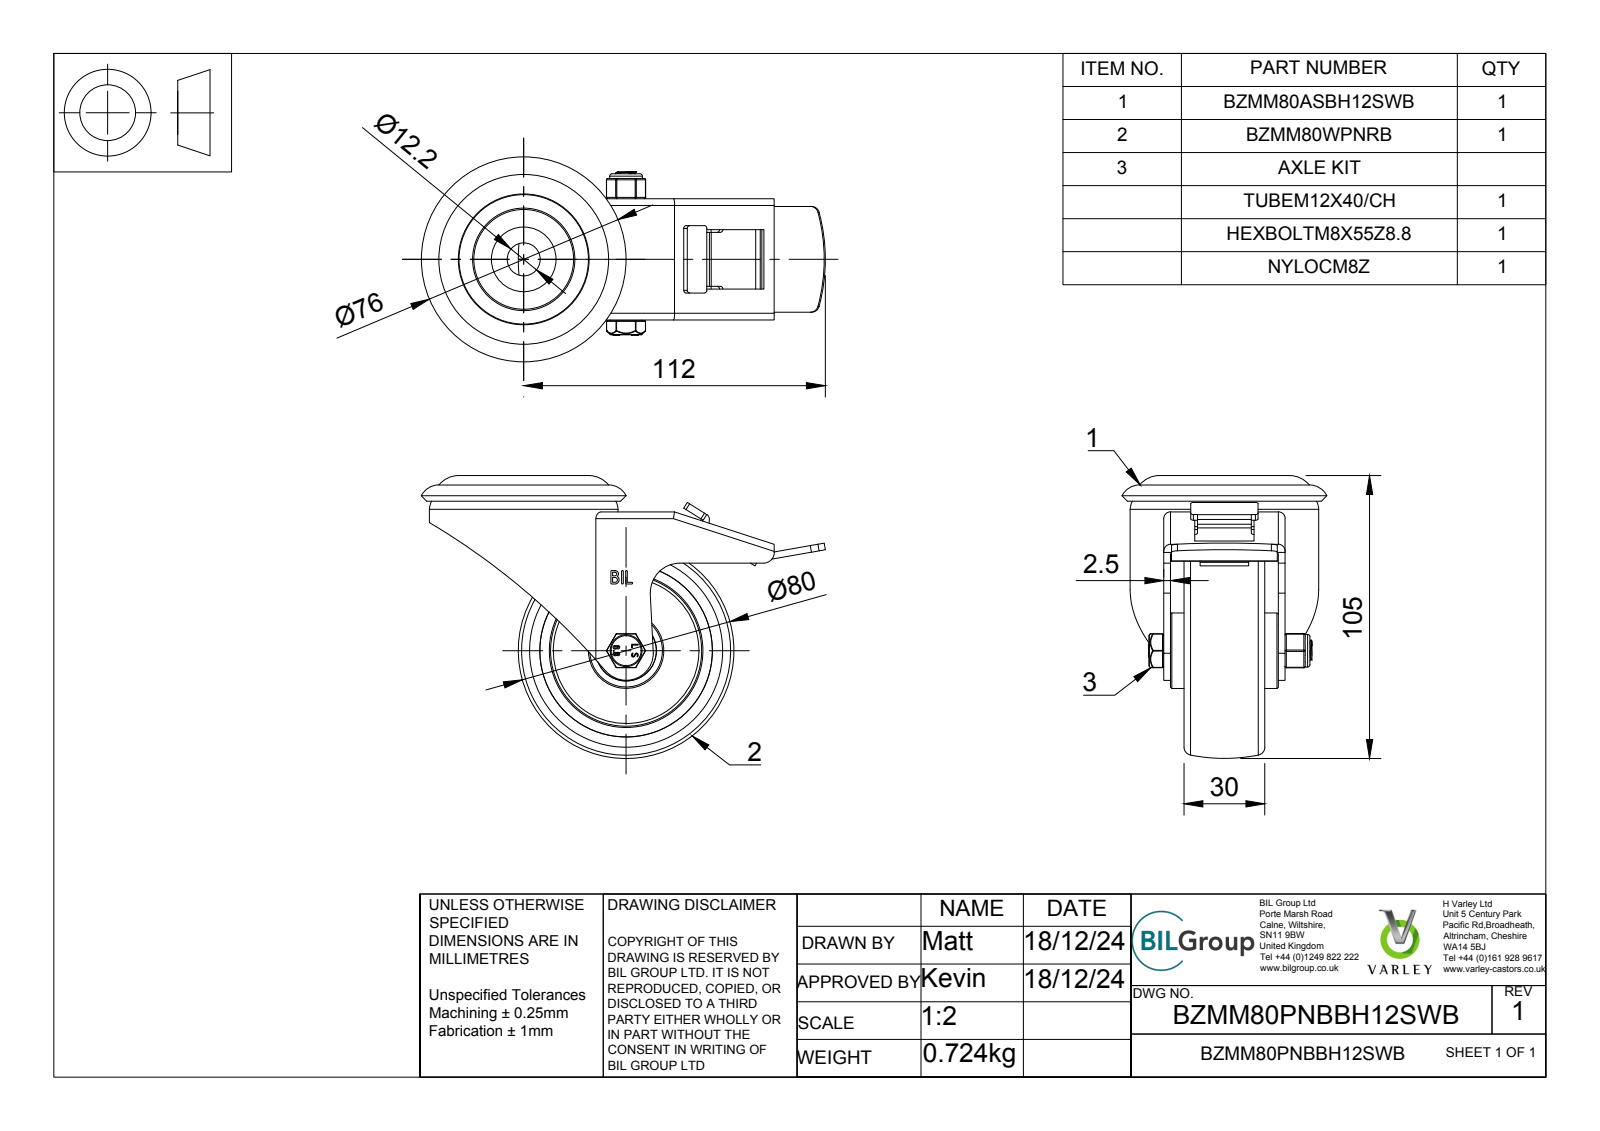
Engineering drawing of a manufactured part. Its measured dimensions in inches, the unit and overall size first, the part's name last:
Units: inches
Overall size (bounding box): 5.906 × 4.134 × 2.992
Round holes (diameter × count): ⌀0.026 ×2, ⌀0.315 ×1, ⌀0.323 ×1, ⌀0.331 ×1, ⌀0.339 ×1, ⌀0.48 ×1, ⌀0.492 ×1, ⌀0.512 ×1, ⌀0.787 ×1, ⌀2.52 ×1, ⌀2.559 ×1, ⌀2.835 ×1
Round bosses / shafts (diameter × count): ⌀0.217 ×6, ⌀2.756 ×1, ⌀1.949 ×1, ⌀1.496 ×1, ⌀1.102 ×1, ⌀0.945 ×1, ⌀0.886 ×1, ⌀0.839 ×1
Partial cylindrical surfaces — rounded edges, fillets, slot ends (radius × count): R0.03 ×48, R0.02 ×26, R0.01 ×12, R0.039 ×6, R0.049 ×6, R0.079 ×5, R0.098 ×5, R0.013 ×4
Main face-to-face distances: 0.098, 0.197, 1.673, 1.378, 0.512, 0.295, 1.476, 0.669, 0.866, 0.807
Hole centre spacings: 0.127, 0.098
Volume: 10.49 in³ · Surface area: 167.8 in²
Bodies: 18 solids, 668 faces (331 planar, 236 cylindrical, 101 other)
Part name (STEP PRODUCT): BZMM80PNBBH12SWB v3; BZMM80ASBH12SWB v1; ZINC PLATED, PRESSED STEEL HEAD; ZINC PLATED, PRESSED STEEL FORKS (+8 more)
STEP written by: Autodesk Translation Framework v13.20.0.188 (AP242_MANAGED_MODEL_BASED_3D_ENGINEERING_MIM_LF)
